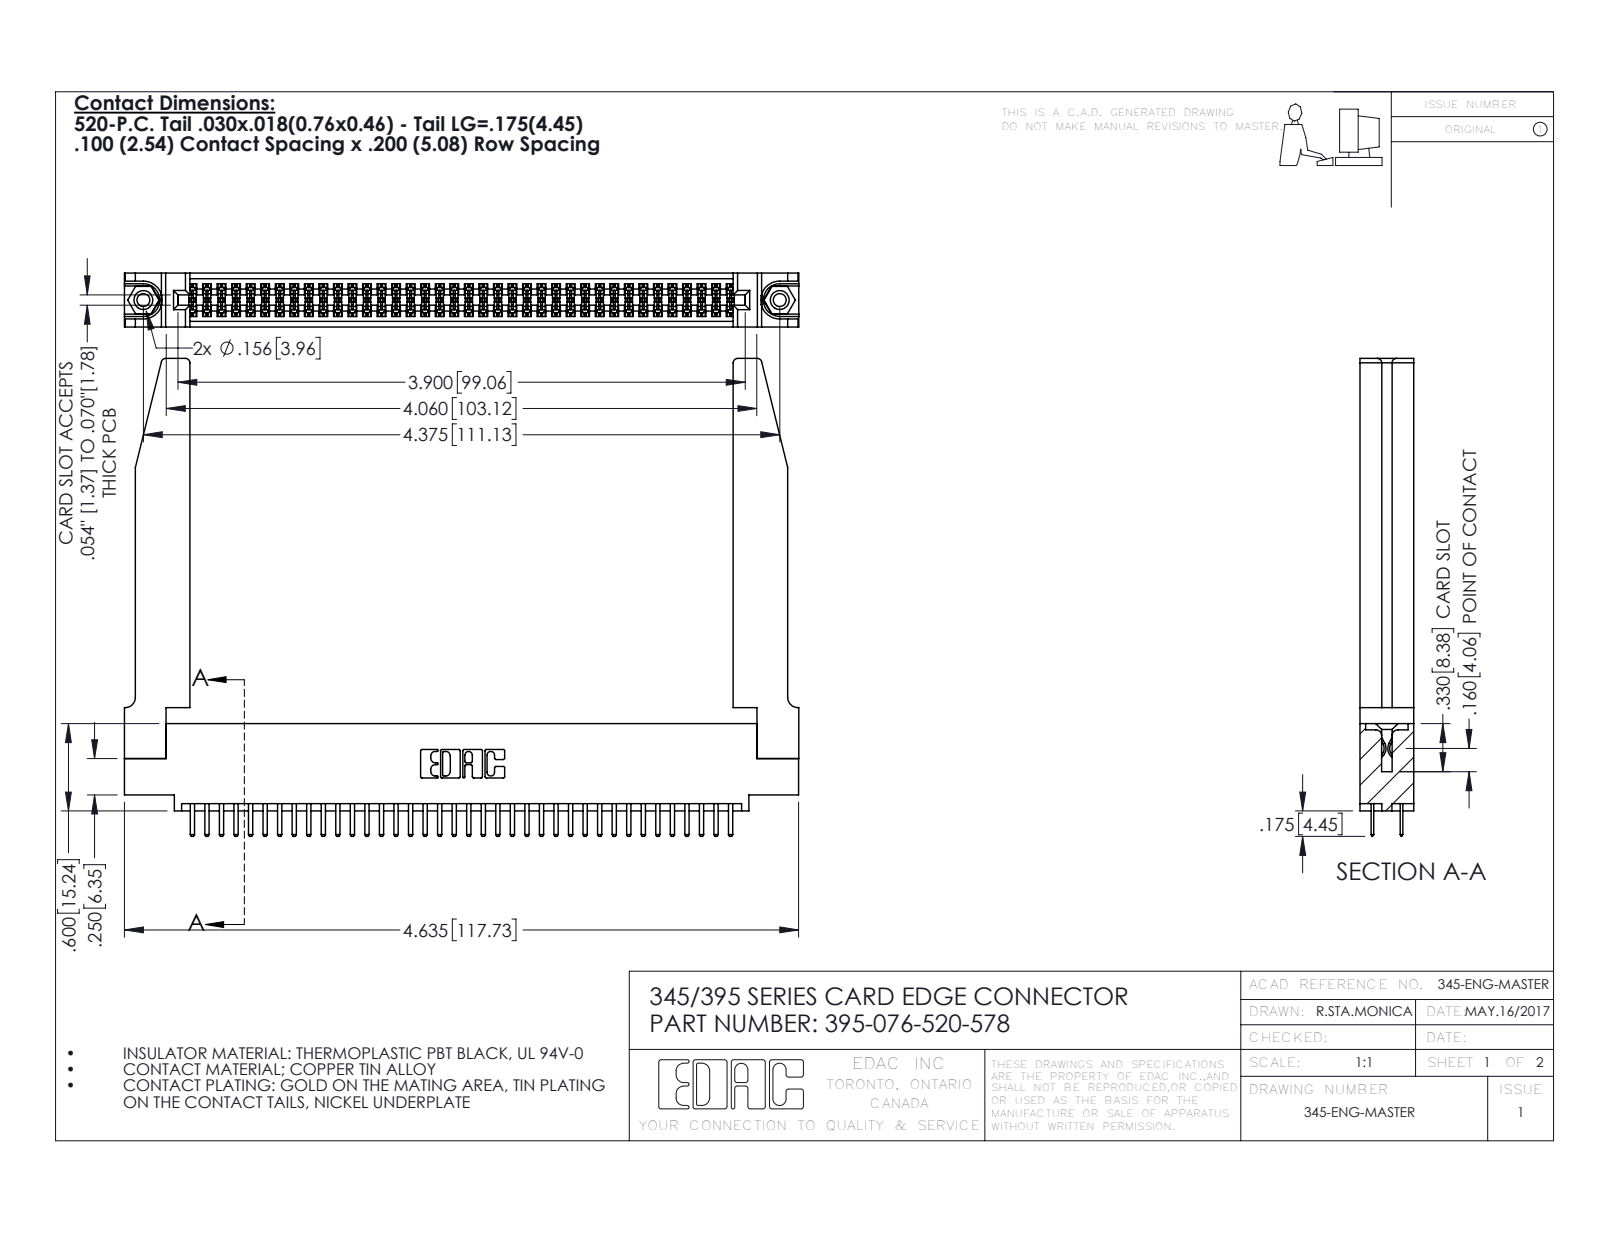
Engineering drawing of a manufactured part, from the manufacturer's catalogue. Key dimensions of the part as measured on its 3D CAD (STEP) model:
Part name (STEP PRODUCT): 345 Part_0.110 Offset - 0.156 Dia-TH; 345-250-001_345-250-001-102; 345-292-001_345-293-120; 395-076-520-578 (+1 more)
STEP written by: SolidWorks 2016 (CONFIG_CONTROL_DESIGN)
Units: inches
Bodies: 81 solids, 4468 faces (2886 planar, 1530 cylindrical, 52 other)
Overall size (bounding box): 4.636 × 3.285 × 0.37
Volume: 1.163 in³ · Surface area: 36.39 in²
Round holes (diameter × count): ⌀0.089 ×2, ⌀0.125 ×2, ⌀0.156 ×2, ⌀0.064 ×1
Round bosses / shafts (diameter × count): ⌀0.155 ×2
Partial cylindrical surfaces — rounded edges, fillets, slot ends (radius × count): R0.006 ×114, R0.01 ×80, R0.01 ×22, R0.03 ×8, R0.007 ×6, R0.031 ×6, R0.026 ×3, R0.014 ×2
Main face-to-face distances: 0.37, 0.072, 0.298, 0.2, 0.098, 0.272, 0.025, 0.225, 0.022, 0.175
Hole centre spacings: 0.27, 4.139, 4.375
